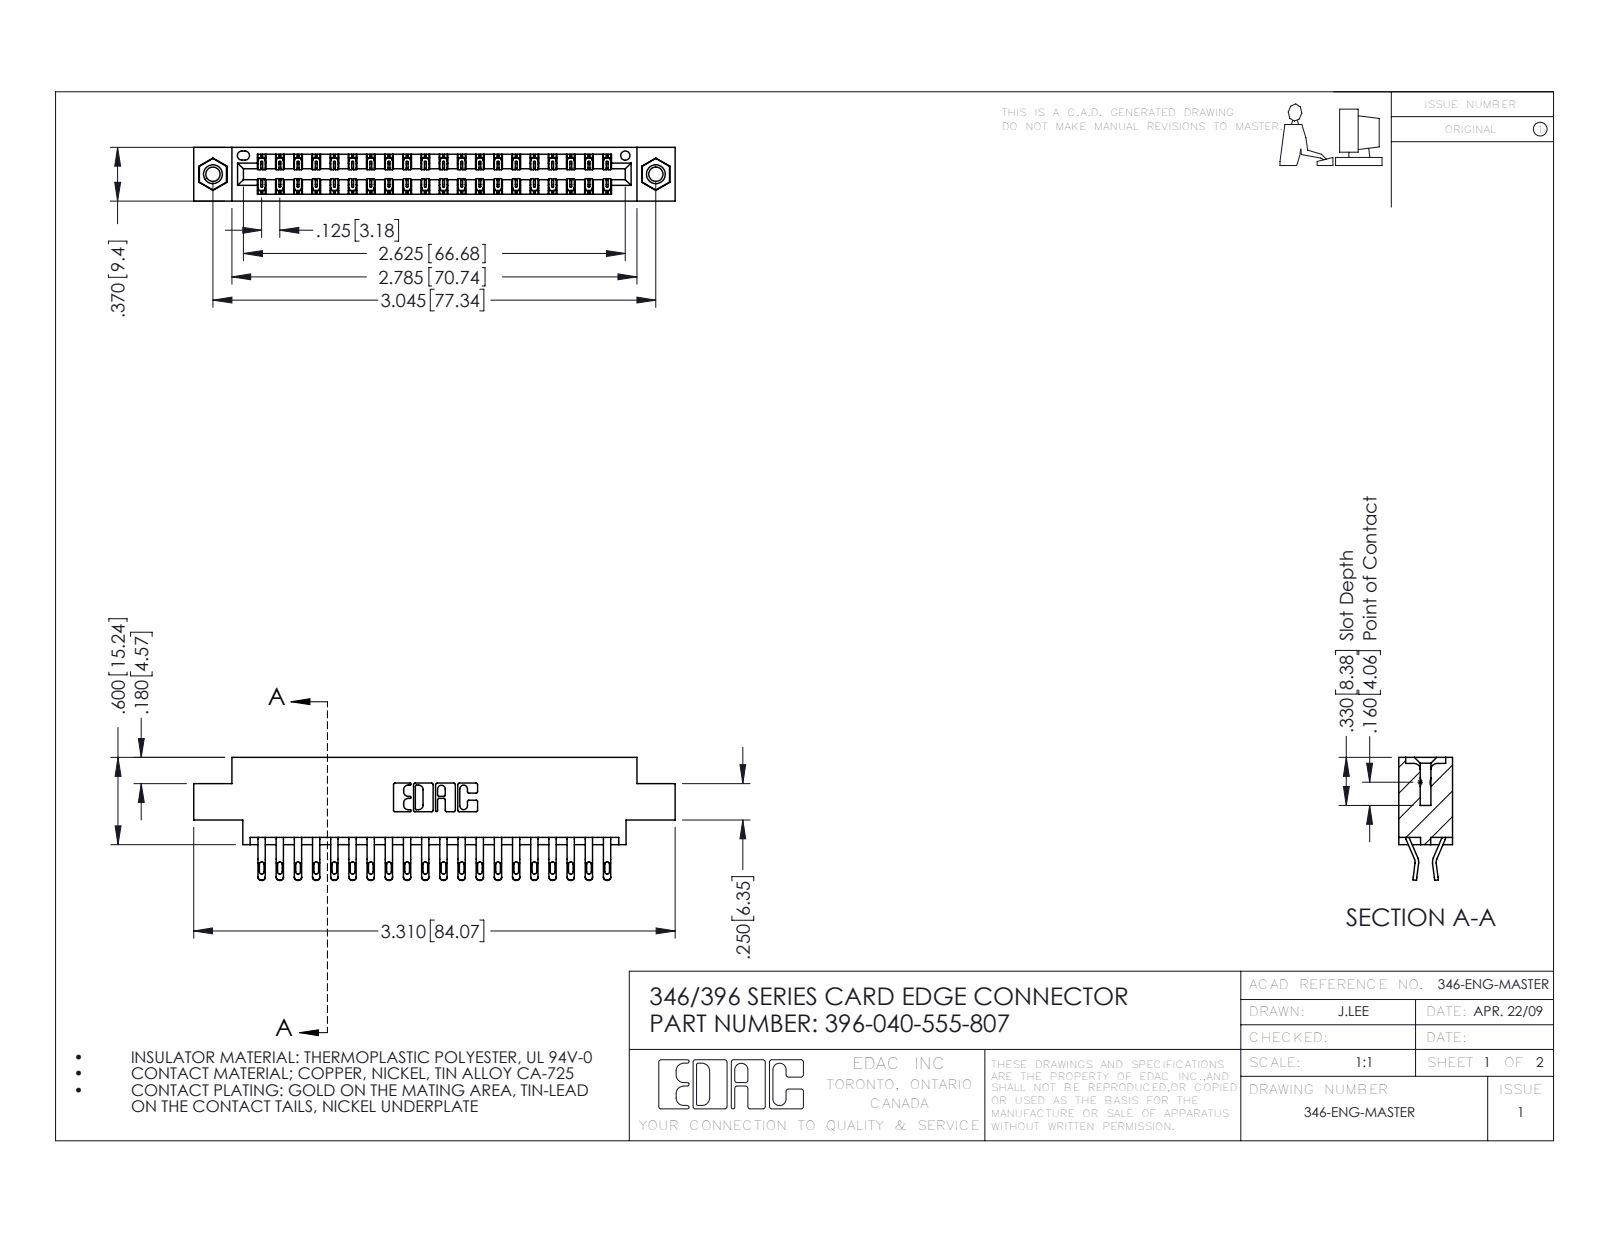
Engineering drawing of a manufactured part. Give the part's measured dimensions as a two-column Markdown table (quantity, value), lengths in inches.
| quantity | value |
| --- | --- |
| part name | 345-250-001_345-250-005-103; 346 Part_0.170 Offset - 0.156 Dia-TI; 345-292-001_555 Tail; 396-040-555-807 |
| STEP written by | SolidWorks 2016 (CONFIG_CONTROL_DESIGN) |
| units | inches |
| bodies | 43 solids, 2506 faces (1432 planar, 1058 cylindrical, 16 other) |
| overall size | 3.31 × 0.845 × 0.37 |
| volume | 0.487 in³ |
| surface area | 17.43 in² |
| round holes (diameter × count) | 0.098 × 2, 0.125 × 2, 0.156 × 2, 0.064 × 1 |
| round bosses / shafts (diameter × count) | 0.155 × 2 |
| partial cylindrical surfaces (radius × count) | 0.016 × 80, 0.02 × 80, 0.006 × 60, 0.01 × 22, 0.007 × 6, 0.031 × 6, 0.026 × 3, 0.01 × 2 |
| main face-to-face distances | 0.048, 0.322, 0.37, 0.25, 0.025, 0.072, 0.298, 0.275, 0.222, 0.148 |
| hole center spacings | 0.246, 2.837, 3.045 |
